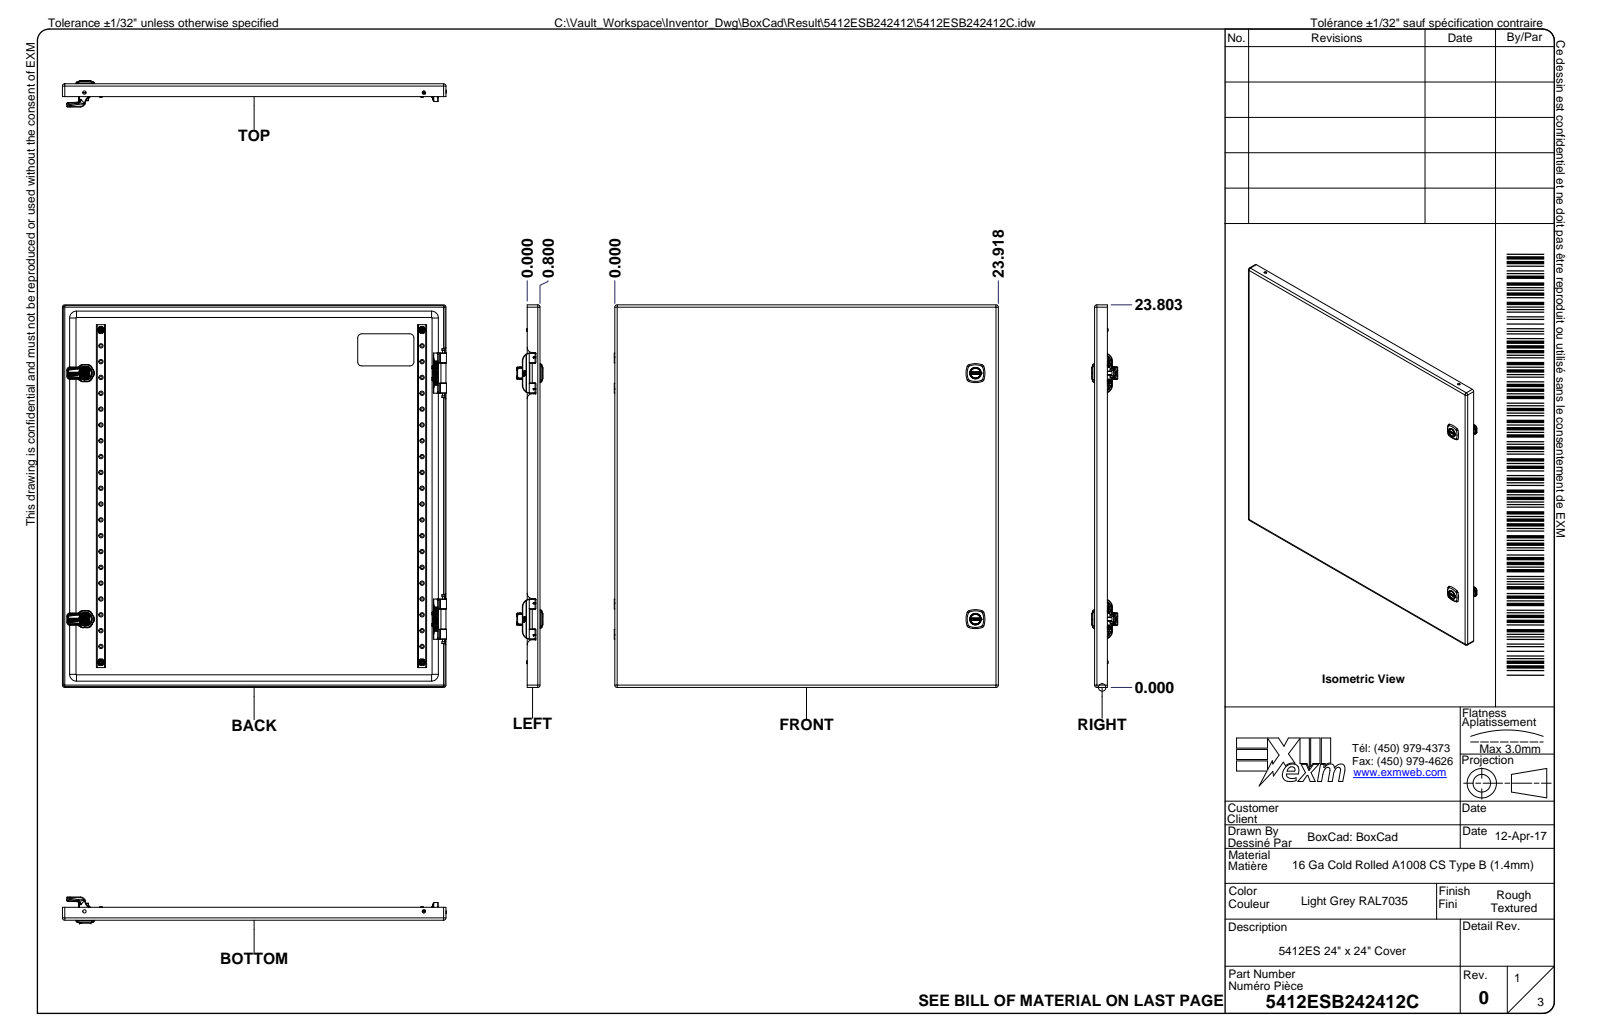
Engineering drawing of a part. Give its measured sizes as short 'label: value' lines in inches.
name: 5412ESB242412; 5412ESB242412B; 5412ESB242412B-P; STK-Q-16005 (+8 more)
written by: Autodesk Inventor 2024 (AUTOMOTIVE_DESIGN)
unit: in
bodies: 64 solids, 10072 faces (3049 planar, 2557 cylindrical, 4466 other)
size: 24.003 × 24 × 13.31
volume: 202.1 in³; area: 6 461 in²
holes: 40× ⌀0.165, 9× ⌀0.03, 8× ⌀0.043, 8× ⌀0.201, 8× ⌀0.315, 6× ⌀0.311, 4× ⌀0.178, 4× ⌀0.197, 4× ⌀0.268, 4× ⌀0.27, 4× ⌀0.29, 4× ⌀0.39
bosses: 40× ⌀0.237, 9× ⌀0.232, 9× ⌀0.03, 8× ⌀0.039, 4× ⌀0.717, 4× ⌀0.374, 4× ⌀0.311, 4× ⌀0.262
rounds: 263× R0.02, 139× R0.01, 105× R0.039, 94× R0.008, 50× R0.012, 32× R0.031, 30× R0.016, 24× R0.084
face distances: 0.053, 23.947, 13.081, 13.028, 24, 23.894, 13.135, 0.927, 0.874, 12.154
hole spacings: 1.969, 0.984, 2.953, 3.937, 21.405, 15.303, 4.921, 5.906
